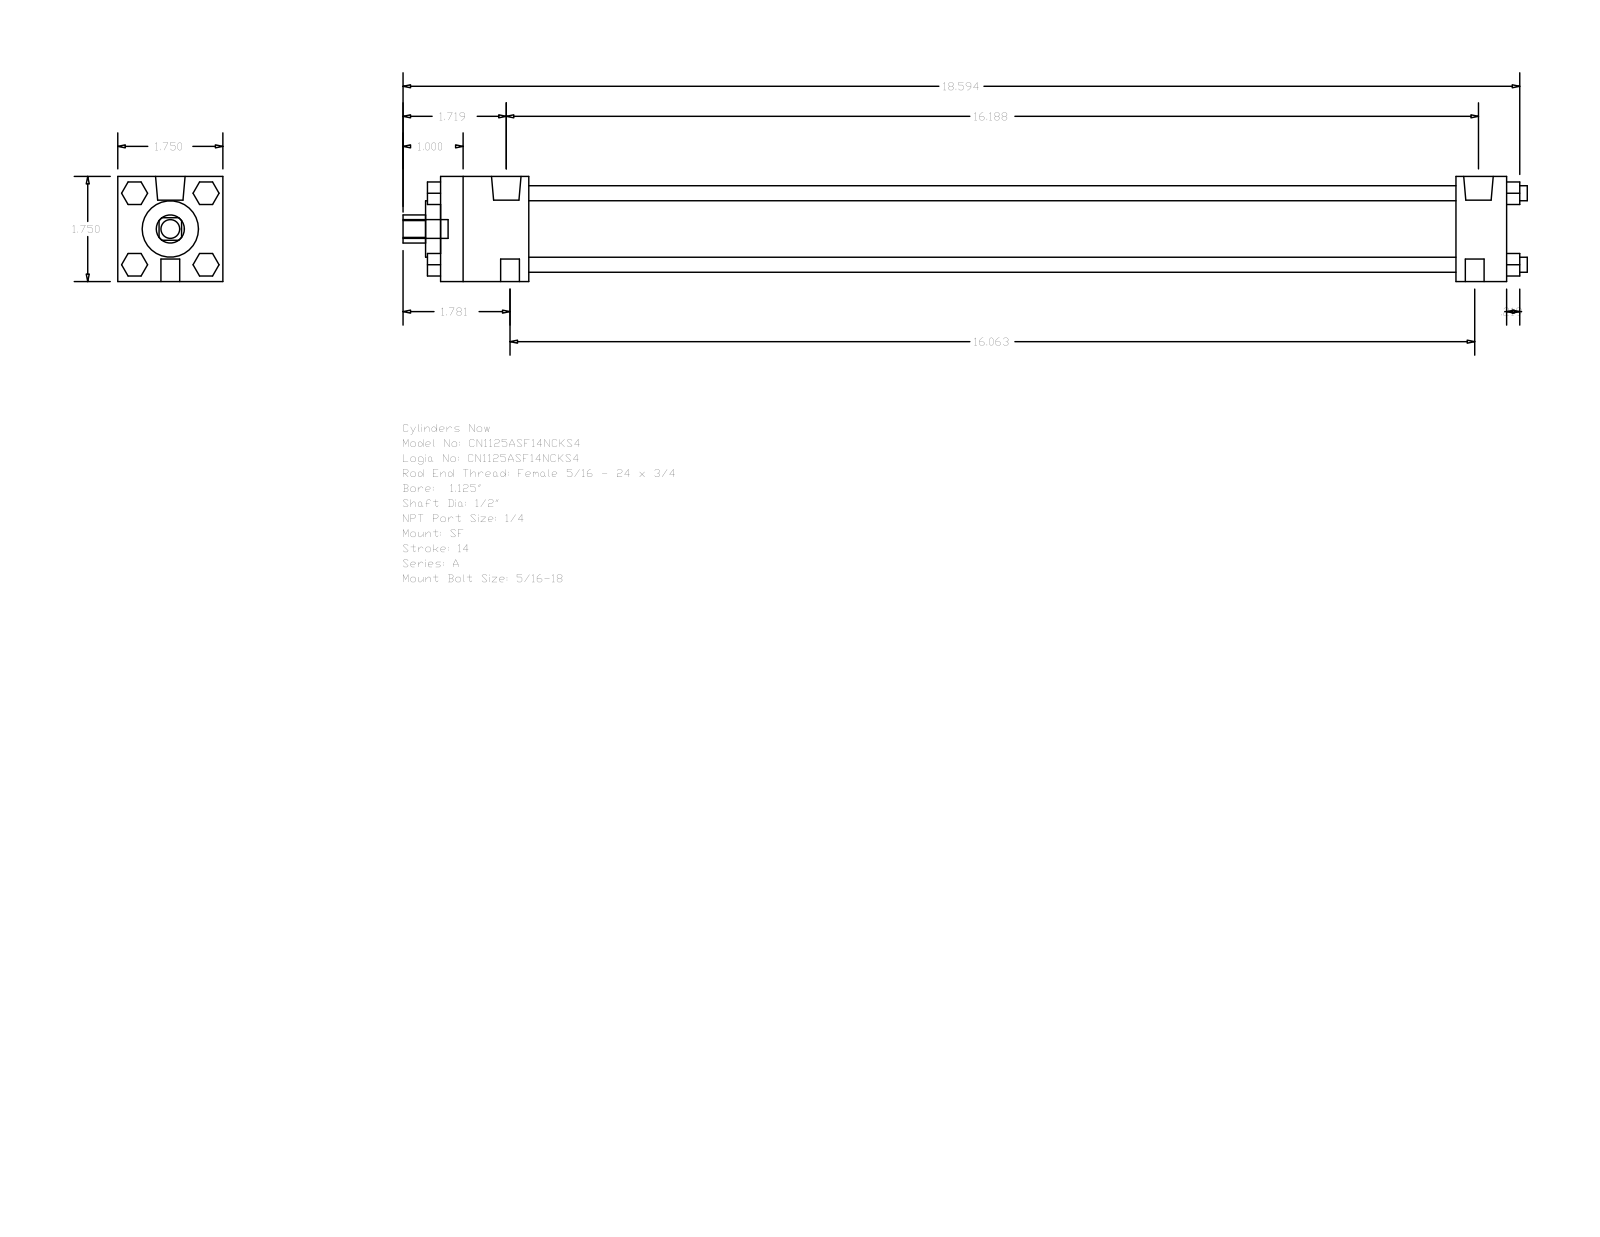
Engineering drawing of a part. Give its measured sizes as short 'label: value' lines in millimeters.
name: A_SF__0112_0.5
written by: GSSL Pune (CONFIG_CONTROL_DESIGN)
unit: mm
bodies: 0 solids, 120 faces (92 planar, 28 cylindrical, 0 other)
size: 475.46 × 44.45 × 44.45
holes: 1× ⌀12.7, 1× ⌀23.81, 1× ⌀31.88
bosses: 4× ⌀6.35, 3× ⌀7.94, 2× ⌀12.49, 2× ⌀5.56
rounds: 1× R5.94
face distances: 44.46, 450.85, 429.41, 21.44, 37.3, 392.11, 413.55, 9.53, 5.59, 9.52
